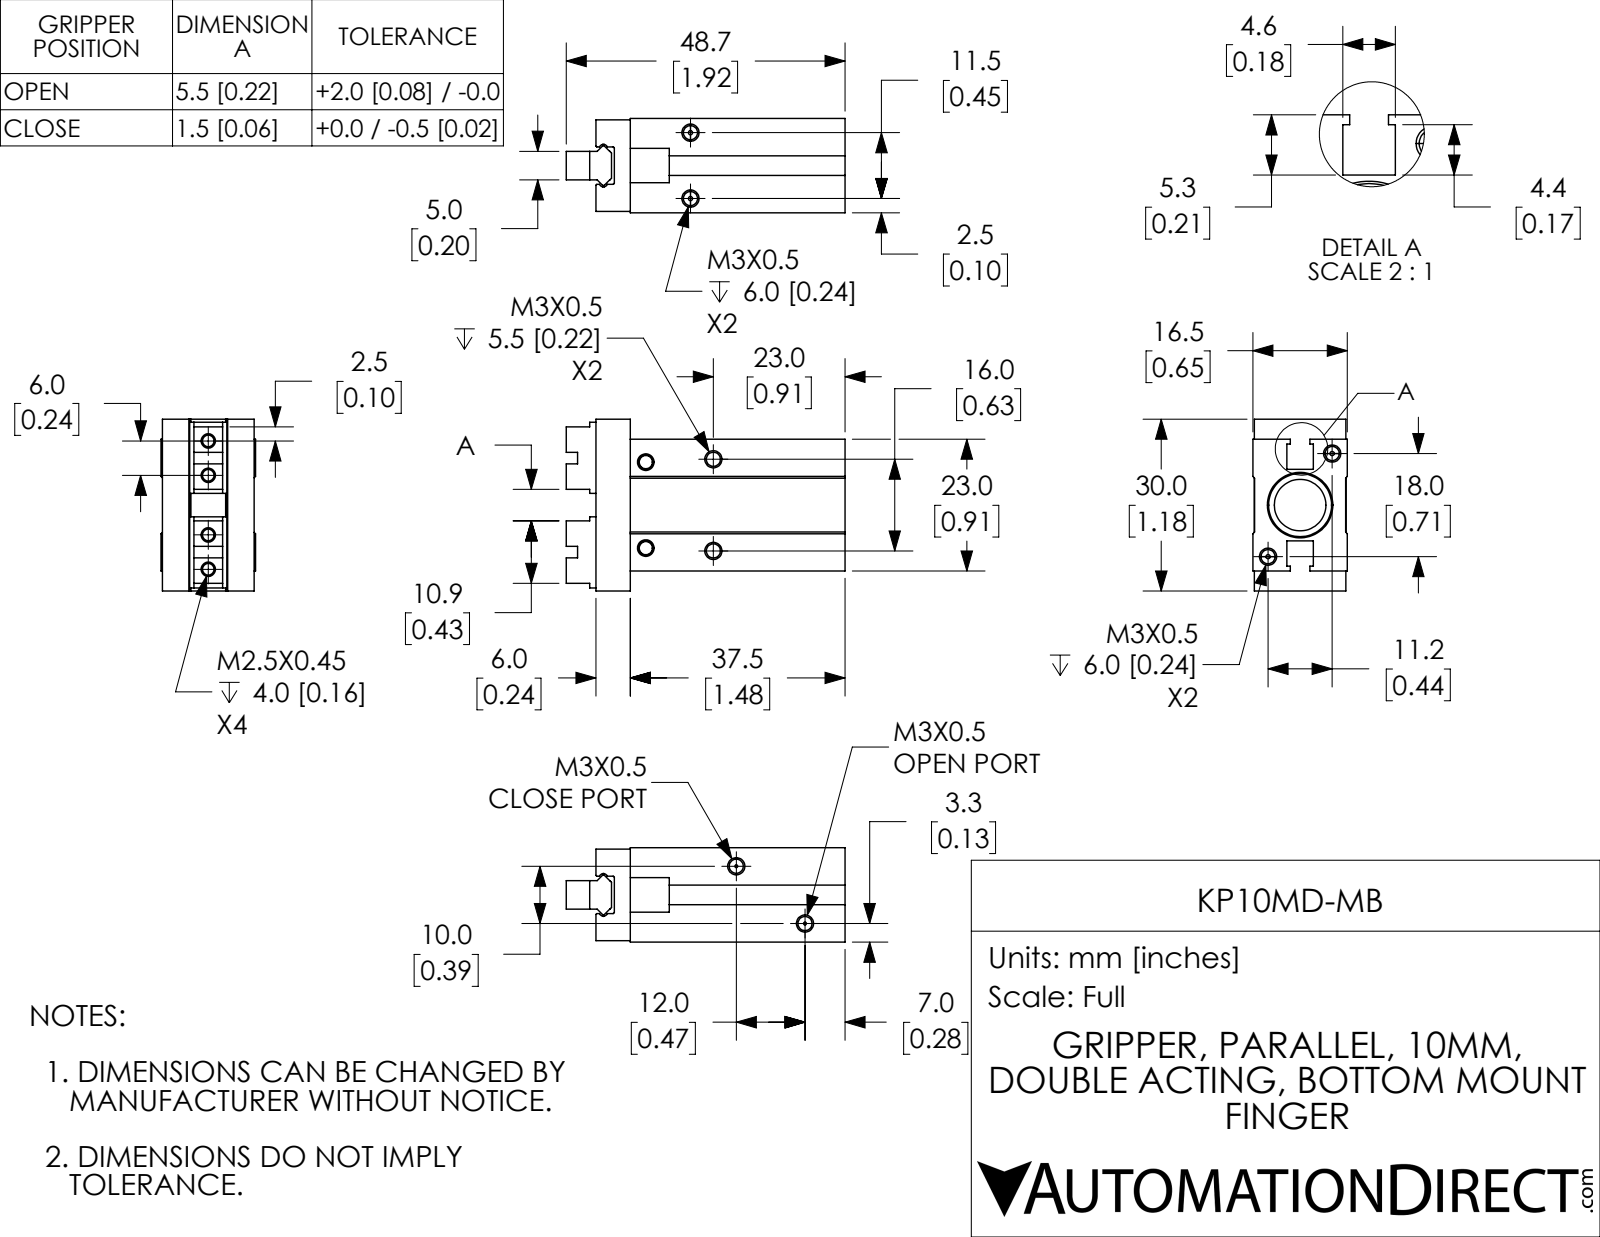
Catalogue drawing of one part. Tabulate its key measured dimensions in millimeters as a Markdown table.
| quantity | value |
| --- | --- |
| part name | KP10MD-MB-3; KP10MD-MB-2; KP10MD-MB-1; KP10MD-MB |
| STEP written by | SolidWorks 2017 (CONFIG_CONTROL_DESIGN) |
| units | millimeters |
| bodies | 3 solids, 228 faces (118 planar, 56 cylindrical, 54 other) |
| overall size | 48.7 × 30 × 16.5 |
| volume | 14 241 mm³ |
| surface area | 7 346 mm² |
| round holes (diameter × count) | 2.46 × 4, 2.46 × 4, 0.5 × 2, 2.01 × 2, 3.02 × 2, 9 × 1, 11 × 1 |
| partial cylindrical surfaces (radius × count) | 0.2 × 4, 0.25 × 2, 0.75 × 2, 1.01 × 2, 1.01 × 2 |
| main face-to-face distances | 16.2, 5.25, 5, 5.65, 5.95, 10.55, 10.25, 5.5, 16.5, 23 |
| hole center spacings | 6.02, 10.6, 11.2, 20.96, 8.04, 11.5, 13.4, 15.62 |
